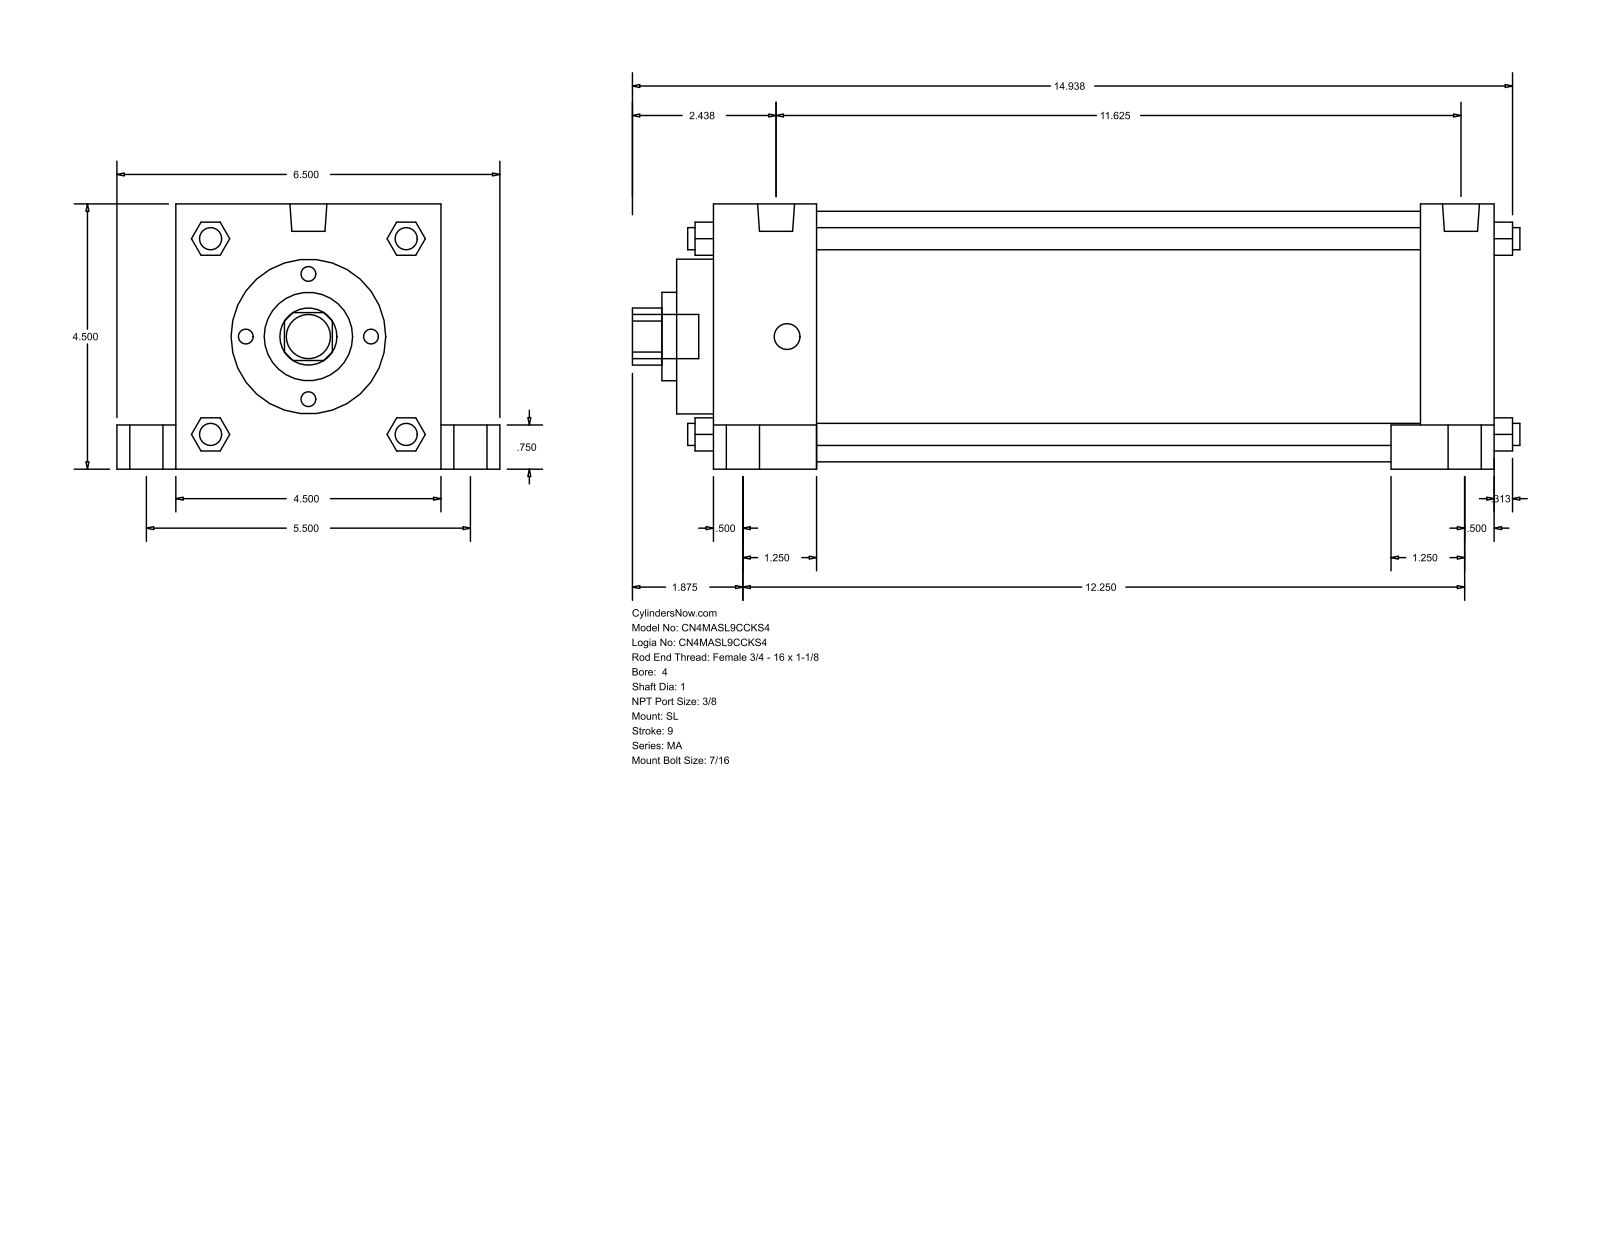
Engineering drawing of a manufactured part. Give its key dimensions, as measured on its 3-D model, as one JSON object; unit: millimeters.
{"part_name": "MA_SL__0400_1", "step_written_by": "GSSL Pune (CONFIG_CONTROL_DESIGN)", "units": "millimeters", "bodies": {"solids": 0, "faces": 150, "planar": 113, "cylindrical": 37, "other": 0}, "overall_size": [382.59, 165.1, 114.3], "round_holes": [[25.4, 1], [38.1, 1], [66.67, 1], [107.95, 1]], "round_bosses_or_shafts": [[20.64, 4], [14.29, 4], [11.11, 4], [9.53, 4], [15.93, 2], [19.05, 1]], "partial_cylinders_radius": [[12.29, 1]], "face_to_face_distances": [114.3, 336.56, 260.35, 44.46, 292.1, 304.81, 31.75, 25.4, 139.7, 19.05]}
